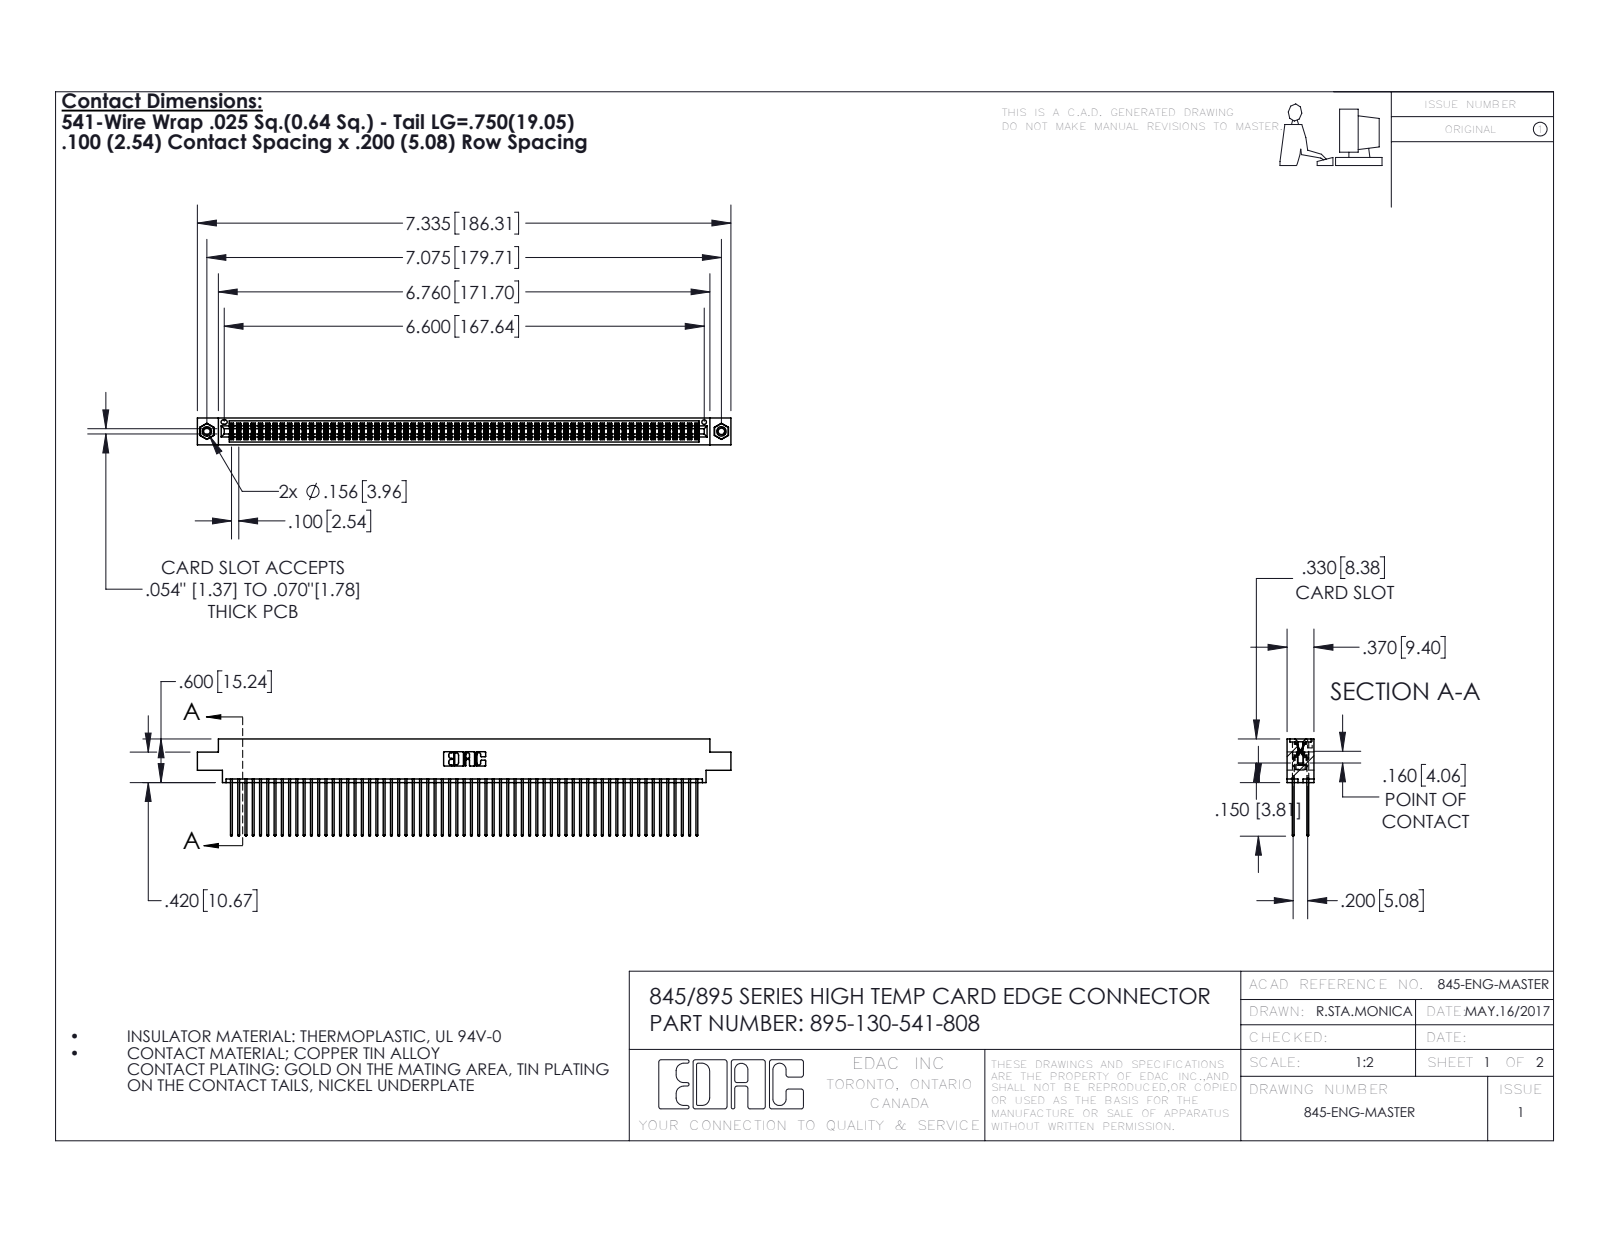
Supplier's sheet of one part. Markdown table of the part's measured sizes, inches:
| quantity | value |
| --- | --- |
| part name | 345-250-001_345-250-003-102; 345-292-001_345-293-141; 395-130-541-808; 345 Part_0.170 Offset - 0.156 Dia-TI |
| STEP written by | SolidWorks 2016 (CONFIG_CONTROL_DESIGN) |
| units | inches |
| bodies | 133 solids, 6690 faces (4406 planar, 2268 cylindrical, 16 other) |
| overall size | 7.335 × 1.337 × 0.37 |
| volume | 1.156 in³ |
| surface area | 49.76 in² |
| round holes (diameter × count) | 0.089 × 2, 0.125 × 2, 0.156 × 2, 0.064 × 1 |
| round bosses / shafts (diameter × count) | 0.155 × 2 |
| partial cylindrical surfaces (radius × count) | 0.006 × 196, 0.01 × 130, 0.01 × 22, 0.007 × 6, 0.031 × 6, 0.026 × 3, 0.014 × 2, 0.019 × 2 |
| main face-to-face distances | 0.072, 0.298, 0.2, 0.098, 0.272, 0.025, 0.225, 0.37, 0.175, 0.149 |
| hole center spacings | 0.27, 6.839, 7.075 |
